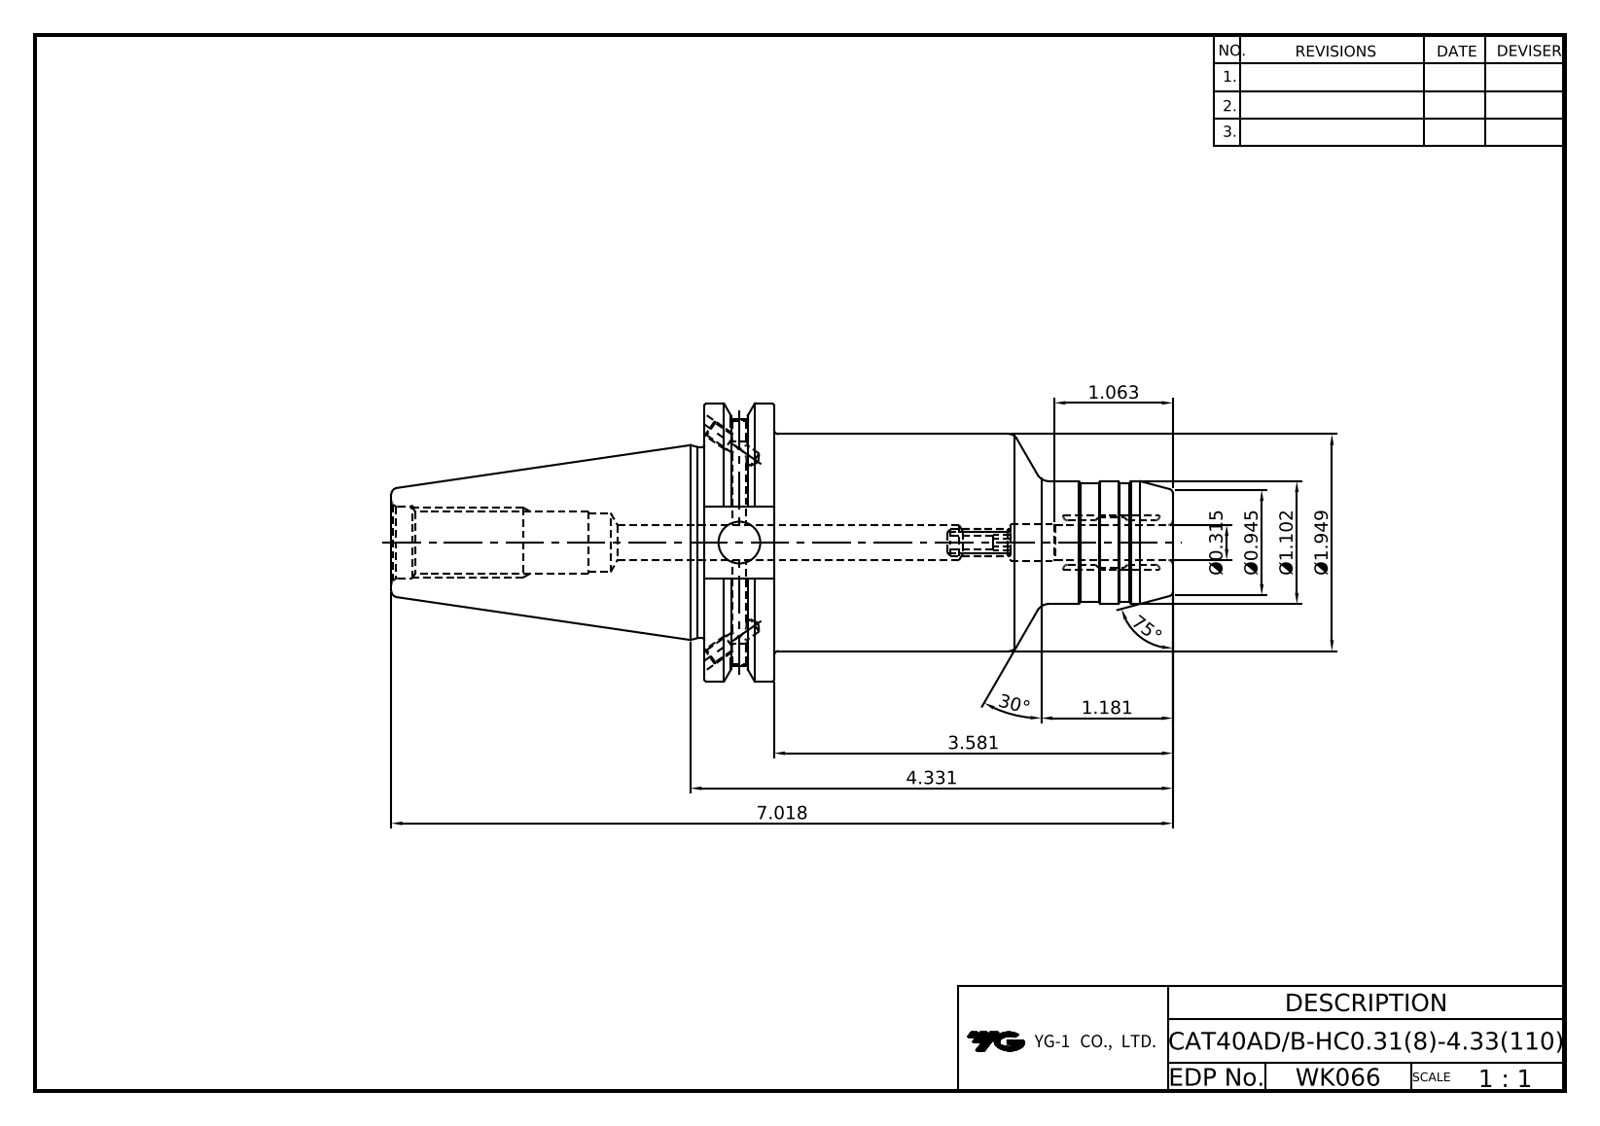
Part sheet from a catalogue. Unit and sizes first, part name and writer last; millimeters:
Units: millimetres
Overall size (bounding box): 178.25 × 63.5 × 61.09
Round holes (diameter × count): ⌀3.24 ×4, ⌀4 ×2, ⌀4.2 ×2, ⌀4.92 ×1, ⌀8 ×1, ⌀8.6 ×1, ⌀9.53 ×1, ⌀13 ×1, ⌀13.39 ×1, ⌀16.3 ×1
Round bosses / shafts (diameter × count): ⌀63.5 ×1, ⌀49.5 ×1, ⌀43.6 ×1, ⌀28 ×1, ⌀27 ×1
Partial cylindrical surfaces — rounded edges, fillets, slot ends (radius × count): R8.19 ×1, R28.15 ×1
Main face-to-face distances: 15.88, 106.83, 90.95, 47.6, 16.38, 71.42, 87.3, 178.25, 77.47, 6.05
Volume: 229 723 mm³ · Surface area: 33 664 mm²
Bodies: 1 solid, 108 faces (34 planar, 36 cylindrical, 38 other)
Part name (STEP PRODUCT): LO-CAT40ADB-HC8-110
STEP written by: Autodesk Inventor 2020 (AUTOMOTIVE_DESIGN)
